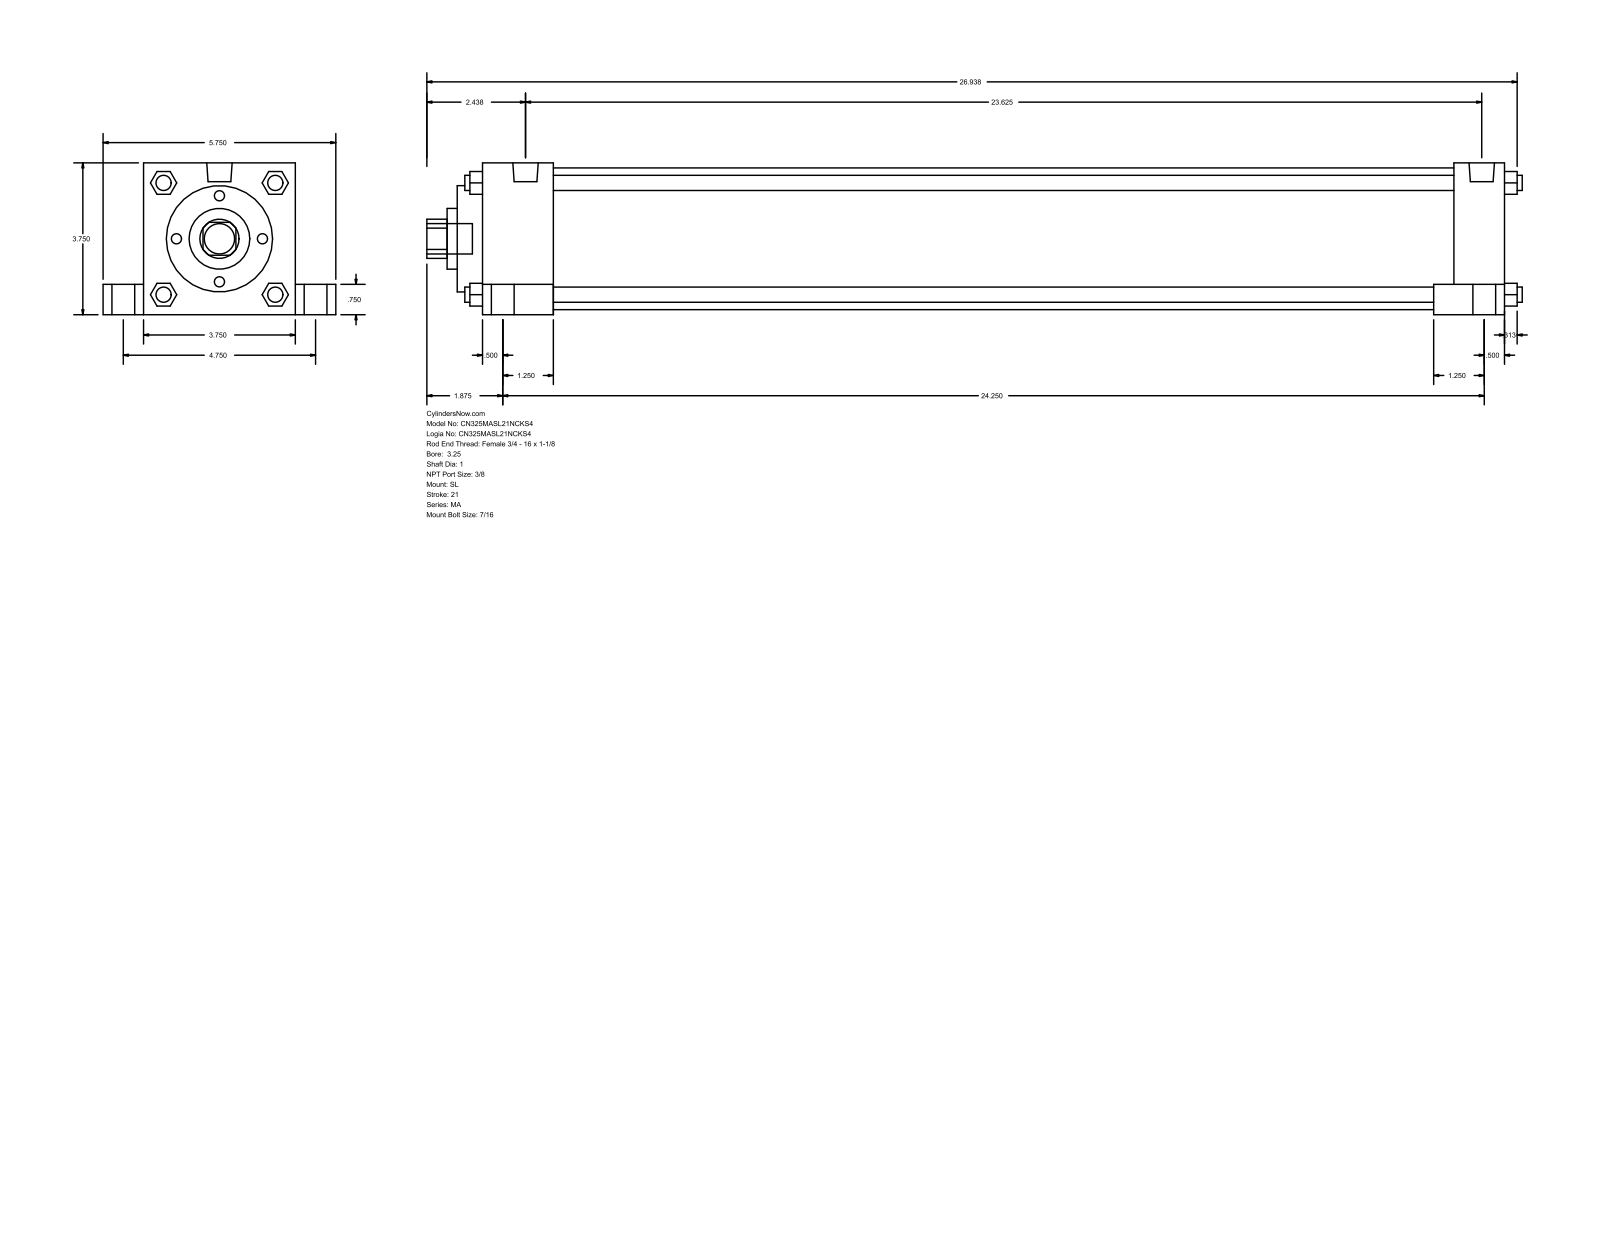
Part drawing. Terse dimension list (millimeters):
name: MA_SL__0325_1
written by: GSSL Pune (CONFIG_CONTROL_DESIGN)
unit: mm
bodies: 0 solids, 150 faces (113 planar, 37 cylindrical, 0 other)
size: 687.39 × 146.05 × 95.25
holes: 1× ⌀25.4, 1× ⌀38.1, 1× ⌀66.67, 1× ⌀88.9
bosses: 4× ⌀20.64, 4× ⌀14.29, 4× ⌀11.11, 4× ⌀9.53, 2× ⌀15.93, 1× ⌀19.05
rounds: 1× R12.29
face distances: 95.24, 641.35, 15.87, 25.41, 120.65, 657.22, 19.05, 609.6, 31.75, 44.46
